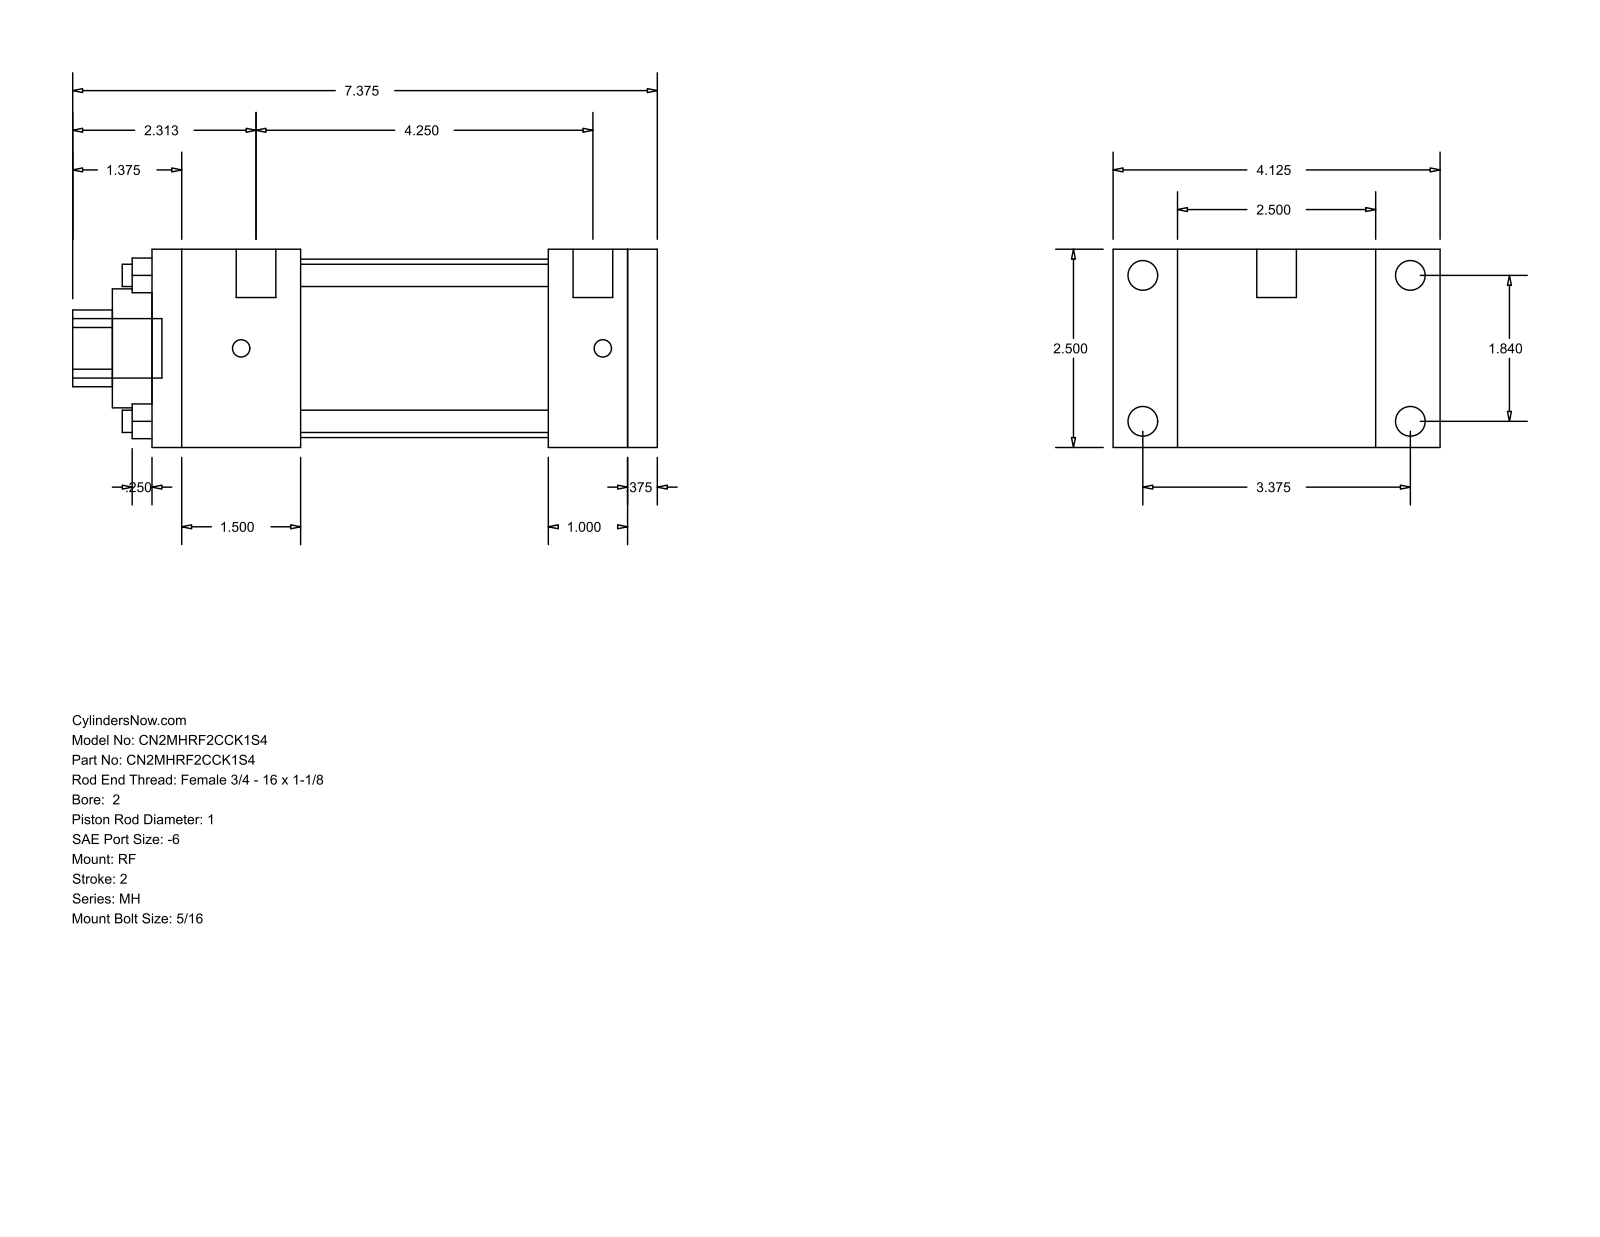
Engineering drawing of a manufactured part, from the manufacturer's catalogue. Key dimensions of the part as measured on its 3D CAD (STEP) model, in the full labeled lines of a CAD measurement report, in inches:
Part name (STEP PRODUCT): MH_RF__0200_1
STEP written by: GSSL Pune (CONFIG_CONTROL_DESIGN)
Units: inches
Bodies: 0 solids, 92 faces (64 planar, 28 cylindrical, 0 other)
Overall size (bounding box): 7.375 × 4.125 × 2.5
Round holes (diameter × count): ⌀0.281 ×4, ⌀1 ×1, ⌀1.5 ×1, ⌀2.25 ×1
Round bosses / shafts (diameter × count): ⌀0.375 ×4, ⌀0.219 ×4, ⌀0.5 ×2, ⌀0.75 ×1
Partial cylindrical surfaces — rounded edges, fillets, slot ends (radius × count): R0.484 ×1
Main face-to-face distances: 2.5, 0.375, 6.375, 6, 0.813, 1, 1.875, 5, 3.125, 4.125
Hole centre spacings: 1.301, 1.84, 2.602
